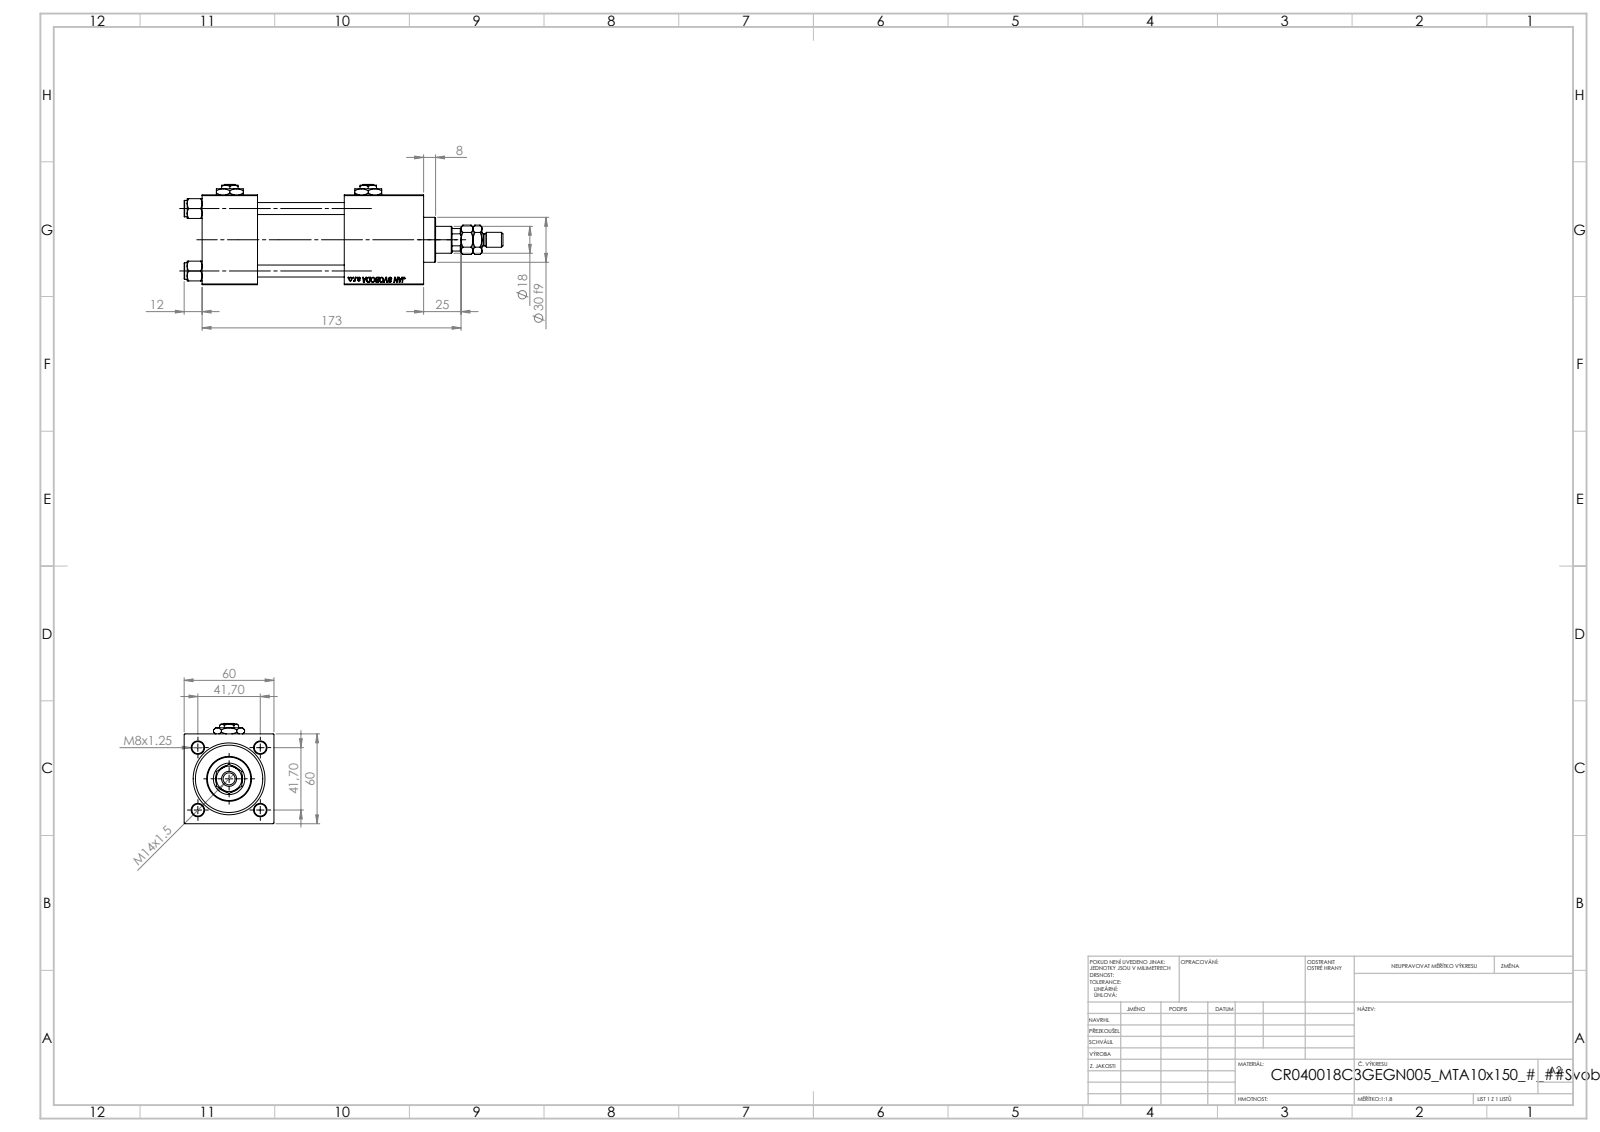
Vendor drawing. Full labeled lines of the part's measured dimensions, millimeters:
Part name (STEP PRODUCT): V215CR_C_TYCINKA; V215_VC_A; V215CR_C_Body; MTA (+3 more)
STEP written by: SolidWorks 2019 (CONFIG_CONTROL_DESIGN)
Units: millimetres
Bodies: 14 solids, 1299 faces (589 planar, 102 cylindrical, 608 other)
Overall size (bounding box): 213 × 67 × 60
Volume: 403 327 mm³ · Surface area: 110 073 mm²
Round holes (diameter × count): ⌀8 ×4, ⌀7 ×2, ⌀16.66 ×2, ⌀24 ×2, ⌀8.5 ×1, ⌀18 ×1, ⌀21 ×1, ⌀31 ×1, ⌀40 ×1, ⌀45 ×1
Round bosses / shafts (diameter × count): ⌀11 ×4, ⌀46 ×1, ⌀30 ×1, ⌀10 ×1, ⌀8 ×1
Partial cylindrical surfaces — rounded edges, fillets, slot ends (radius × count): R8.5 ×1
Main face-to-face distances: 60, 37, 53, 148, 111, 58, 95, 119.3, 82.3, 24.3
Hole centre spacings: 29.49, 41.7, 58.97, 92.5
